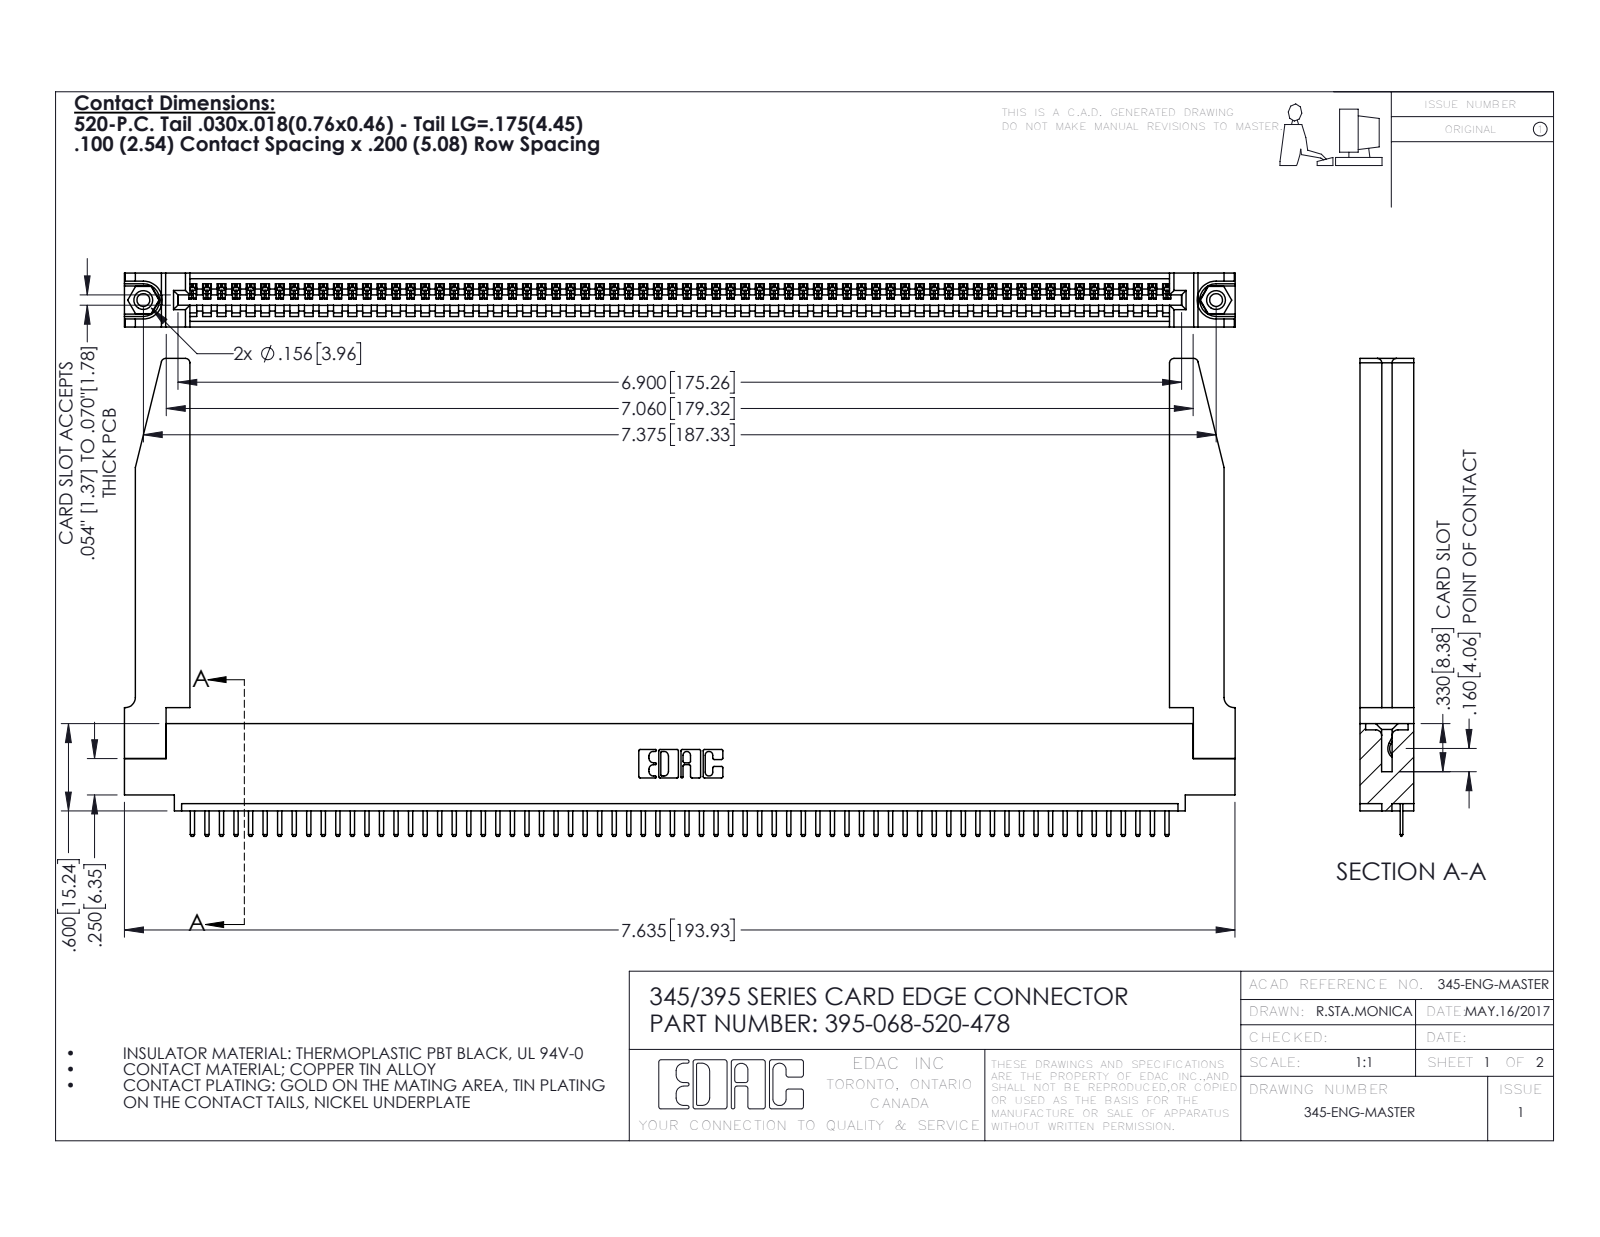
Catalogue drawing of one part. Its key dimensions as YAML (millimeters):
part_name: "345 Part_0.110 Offset - 0.156 Dia-TH; 395-068-520-478; 345-220-078_345-220-078; 345-292-001_345-293-120 (+1 more)"
step_written_by: "SolidWorks 2016 (CONFIG_CONTROL_DESIGN)"
units: millimeters
bodies: {solids: 73, faces: 4580, planar: 3082, cylindrical: 1446, other: 52}
overall_size: [194, 83.4, 9.4]
volume: 26140
surface_area: 31050
round_holes:
  - {diameter: 2.3, count: 2}
  - {diameter: 3.2, count: 2}
  - {diameter: 4, count: 2}
  - {diameter: 1.6, count: 1}
round_bosses_or_shafts:
  - {diameter: 3.9, count: 2}
partial_cylinders:
  - {radius: 0.3, count: 138}
  - {radius: 0.2, count: 136}
  - {radius: 0.3, count: 22}
  - {radius: 0.8, count: 8}
  - {radius: 0.2, count: 6}
  - {radius: 0.8, count: 6}
  - {radius: 0.7, count: 3}
  - {radius: 0.8, count: 2}
face_to_face_distances: [9.4, 1.8, 7.6, 2.5, 6.9, 0.6, 5.1, 5.7, 1.8, 3.8]
hole_center_spacings: [6.9, 181.3, 187.3]
